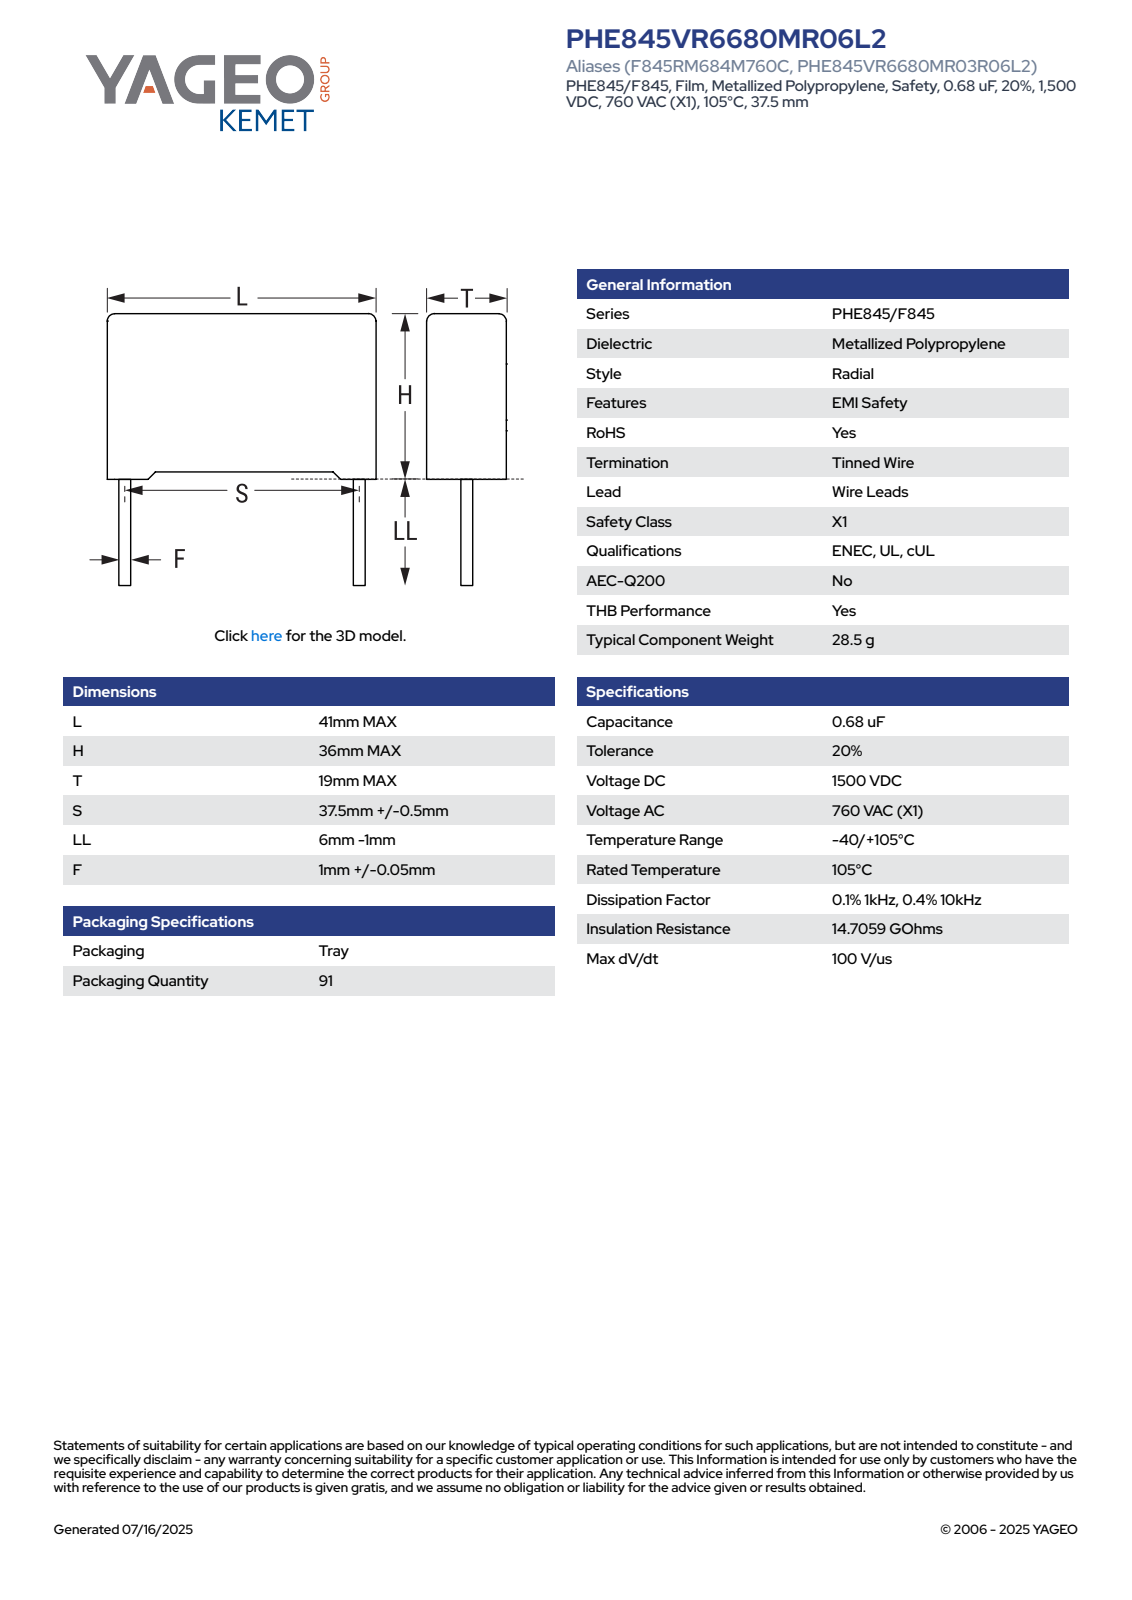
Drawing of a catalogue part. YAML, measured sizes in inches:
part_name: "CFR_RB2_41X36X19_L41H36T19S37.5LL5F1.05"
step_written_by: "SolidWorks 2021 (AUTOMOTIVE_DESIGN)"
units: inches
bodies: {solids: 4, faces: 87, planar: 79, cylindrical: 8, other: 0}
overall_size: [1.614, 1.614, 0.748]
volume: 1.66
surface_area: 9.257
round_bosses_or_shafts:
  - {diameter: 0.041, count: 2}
partial_cylinders:
  - {radius: 0.02, count: 4}
face_to_face_distances: [0.748, 1.614, 1.369, 0.019, 1.388, 0.03, 0.049, 1.417, 0.748, 0.054]
